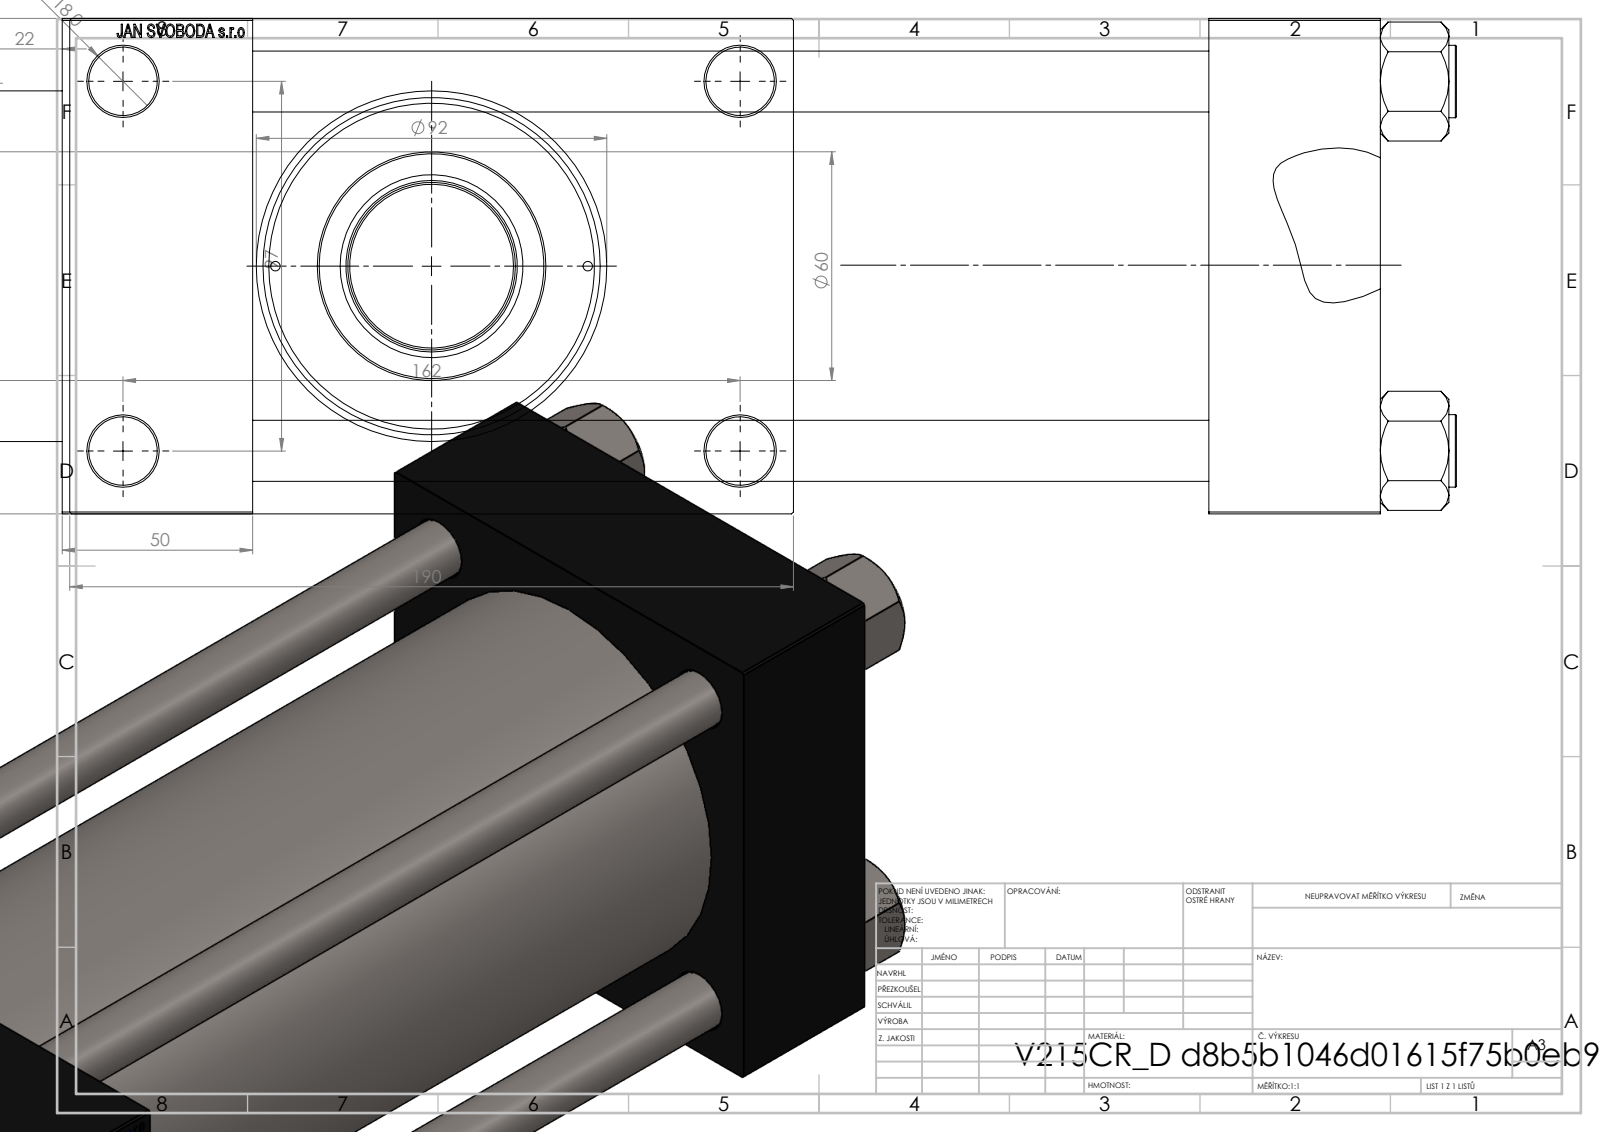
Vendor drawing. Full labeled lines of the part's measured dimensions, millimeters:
Part name (STEP PRODUCT): V215CR_ROD_END_F; NUT_M5_D; V215CR_VCP_D; V215CR_D_Body (+2 more)
STEP written by: SolidWorks 2019 (CONFIG_CONTROL_DESIGN)
Units: millimetres
Bodies: 12 solids, 1172 faces (550 planar, 96 cylindrical, 526 other)
Overall size (bounding box): 467 × 190 × 130
Volume: 3 248 000 mm³ · Surface area: 541 229 mm²
Round holes (diameter × count): ⌀16 ×4, ⌀18 ×4, ⌀2.5 ×2, ⌀7 ×2, ⌀26.44 ×2, ⌀35 ×2, ⌀31.5 ×1, ⌀45 ×1, ⌀48 ×1, ⌀76 ×1, ⌀85.5 ×1, ⌀100 ×1
Round bosses / shafts (diameter × count): ⌀19 ×4, ⌀106 ×1, ⌀92 ×1, ⌀60 ×1, ⌀44 ×1, ⌀33 ×1
Main face-to-face distances: 130, 45, 296, 251, 346, 301, 50, 30, 160, 96
Hole centre spacings: 32.55, 49.02, 62.87, 68.52, 94.41, 96.9, 101.73, 102.27
